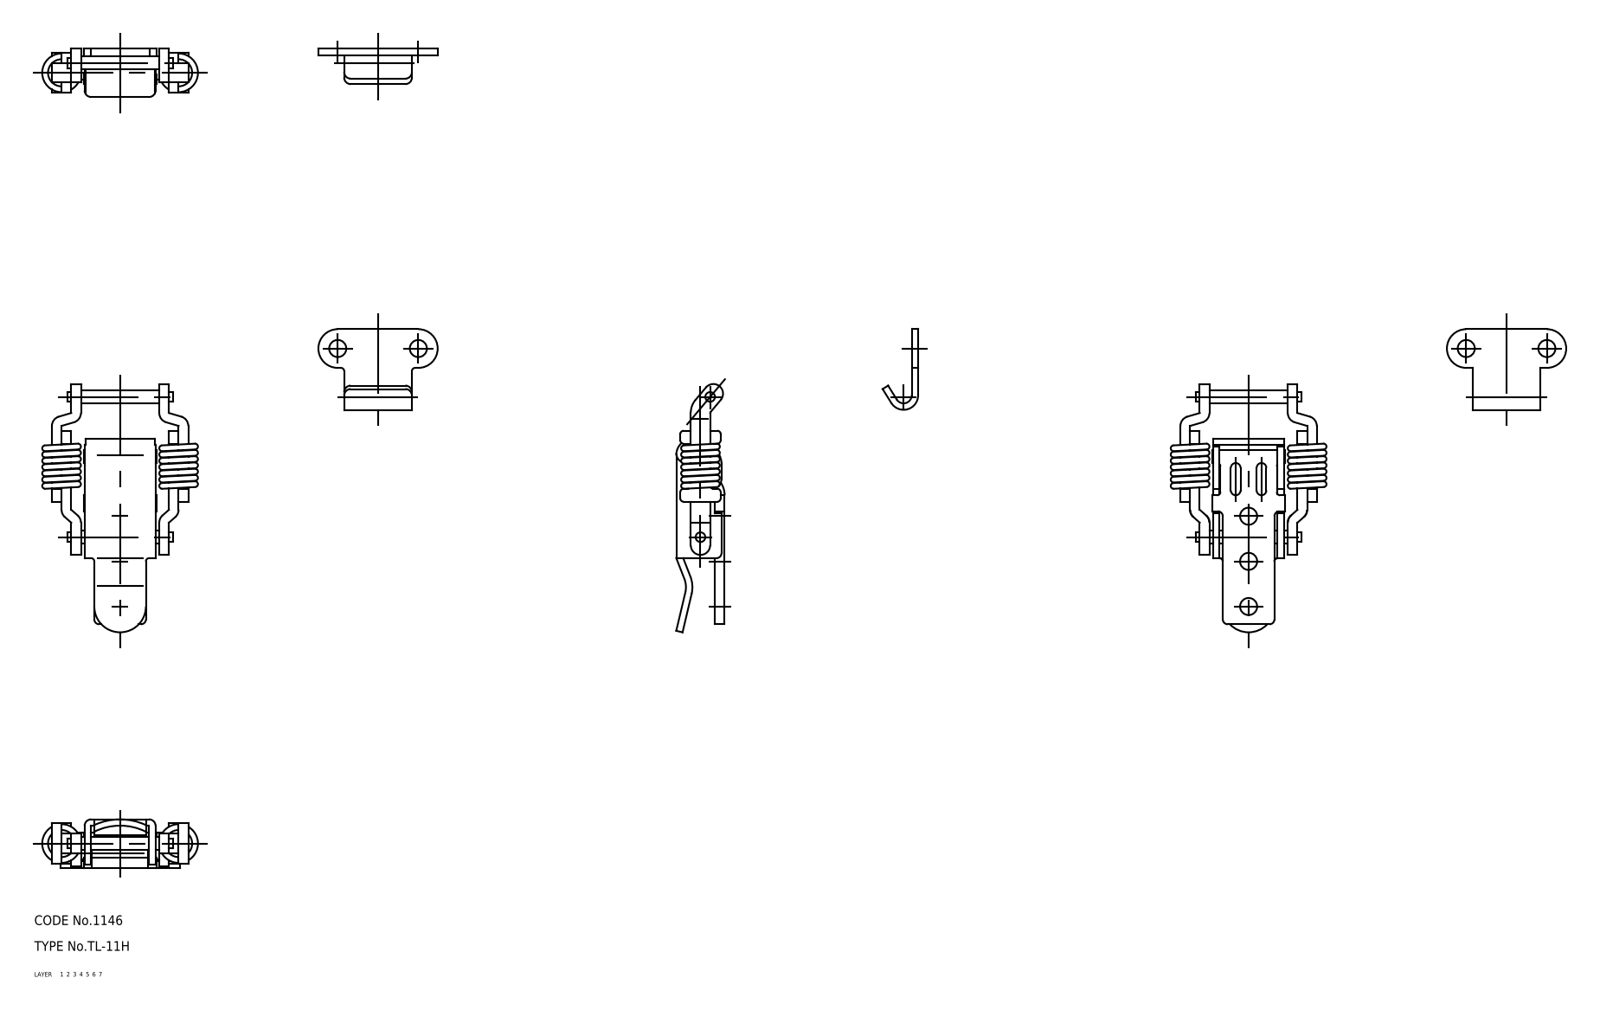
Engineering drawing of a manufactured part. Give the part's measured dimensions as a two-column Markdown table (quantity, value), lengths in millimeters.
| quantity | value |
| --- | --- |
| part name | shaft; spring; arm_B_mr; arm_A_mr (+6 more) |
| STEP written by | CADfix (AUTOMOTIVE_DESIGN) |
| units | millimeters |
| bodies | 11 solids, 289 faces (0 planar, 0 cylindrical, 289 other) |
| overall size | 94 × 48.21 × 15.01 |
| volume | 13 159 mm³ |
| surface area | 15 424 mm² |
